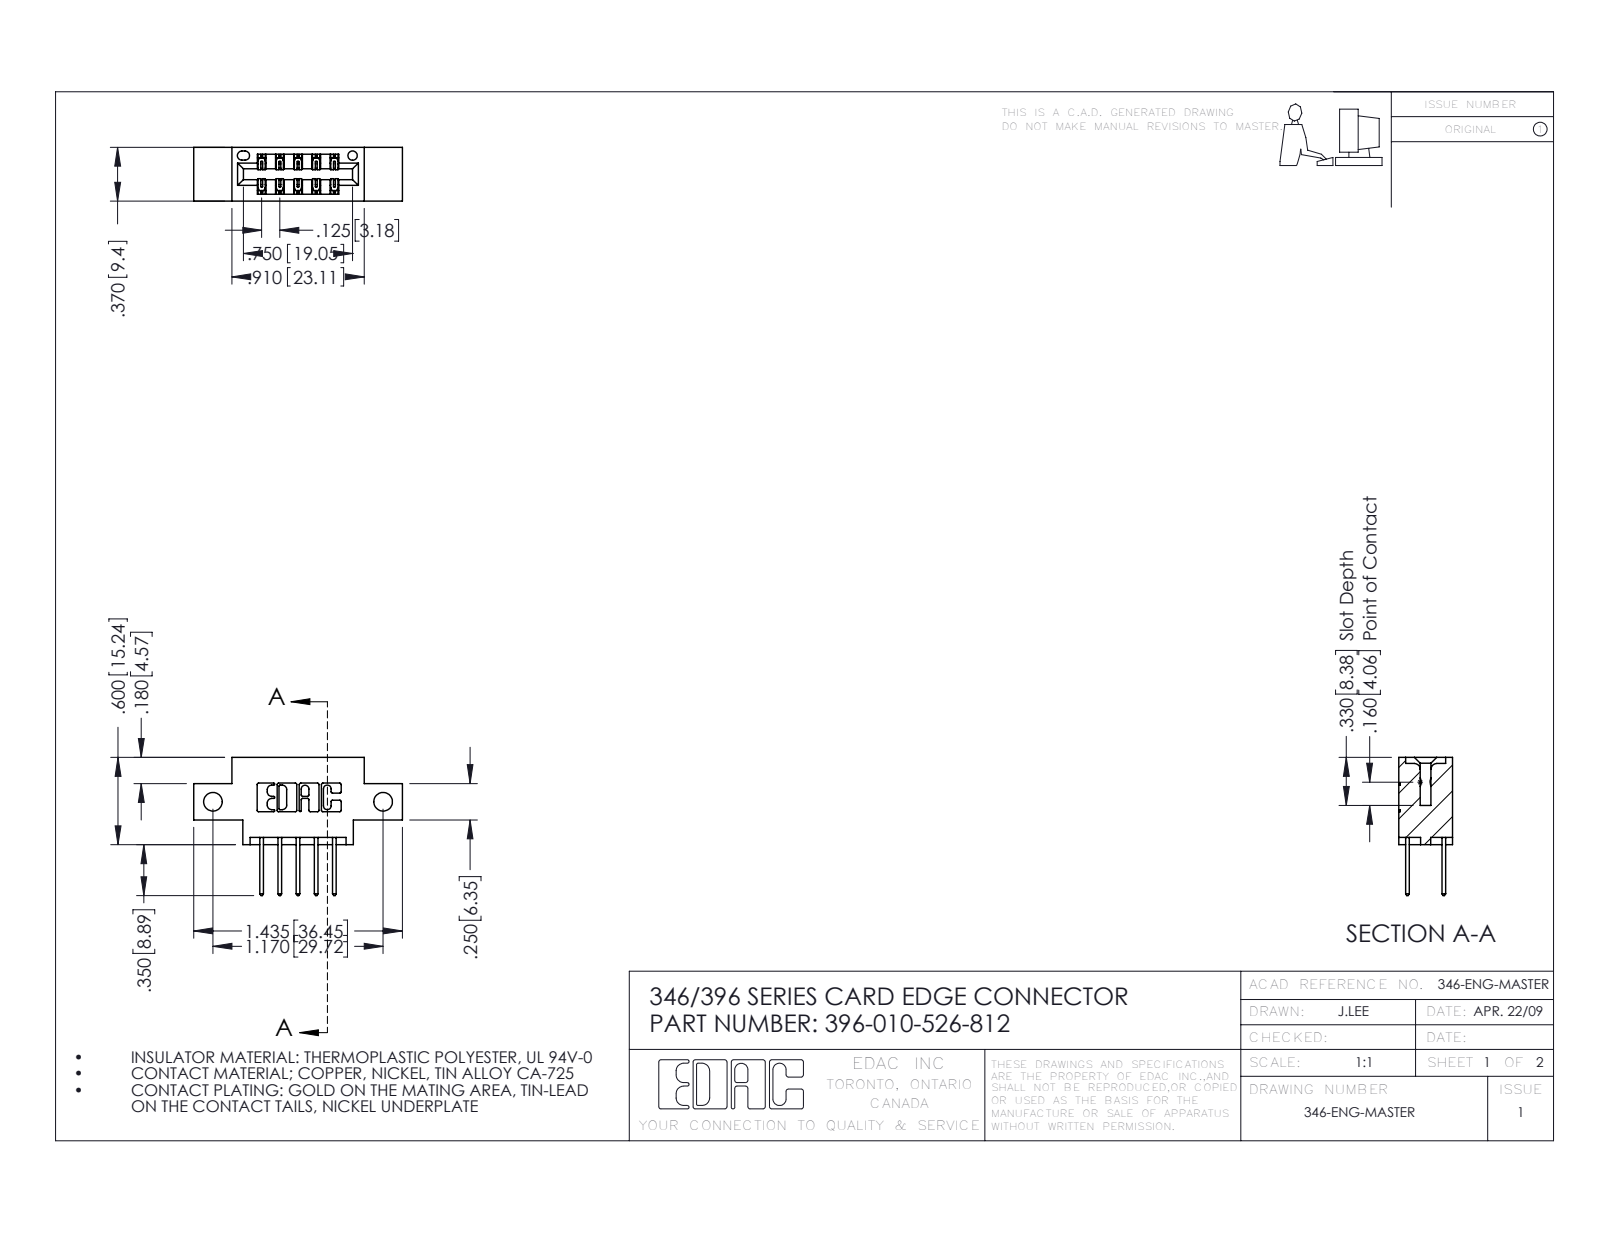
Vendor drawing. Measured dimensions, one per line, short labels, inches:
name: 345-292-001_345-293-126; 396-010-526-812; 346 Part_0.170 Offset - Side Mount
written by: SolidWorks 2016 (CONFIG_CONTROL_DESIGN)
unit: in
bodies: 11 solids, 646 faces (430 planar, 216 cylindrical, 0 other)
size: 1.435 × 0.95 × 0.37
volume: 0.186 in³; area: 5.758 in²
holes: 2× ⌀0.128, 1× ⌀0.064
rounds: 22× R0.01, 15× R0.006, 10× R0.01, 6× R0.007, 6× R0.031, 3× R0.026, 2× R0.014, 2× R0.022
face distances: 0.25, 0.37, 0.048, 0.322, 0.025, 0.072, 0.298, 0.275, 0.225, 0.148
hole spacings: 1.17
